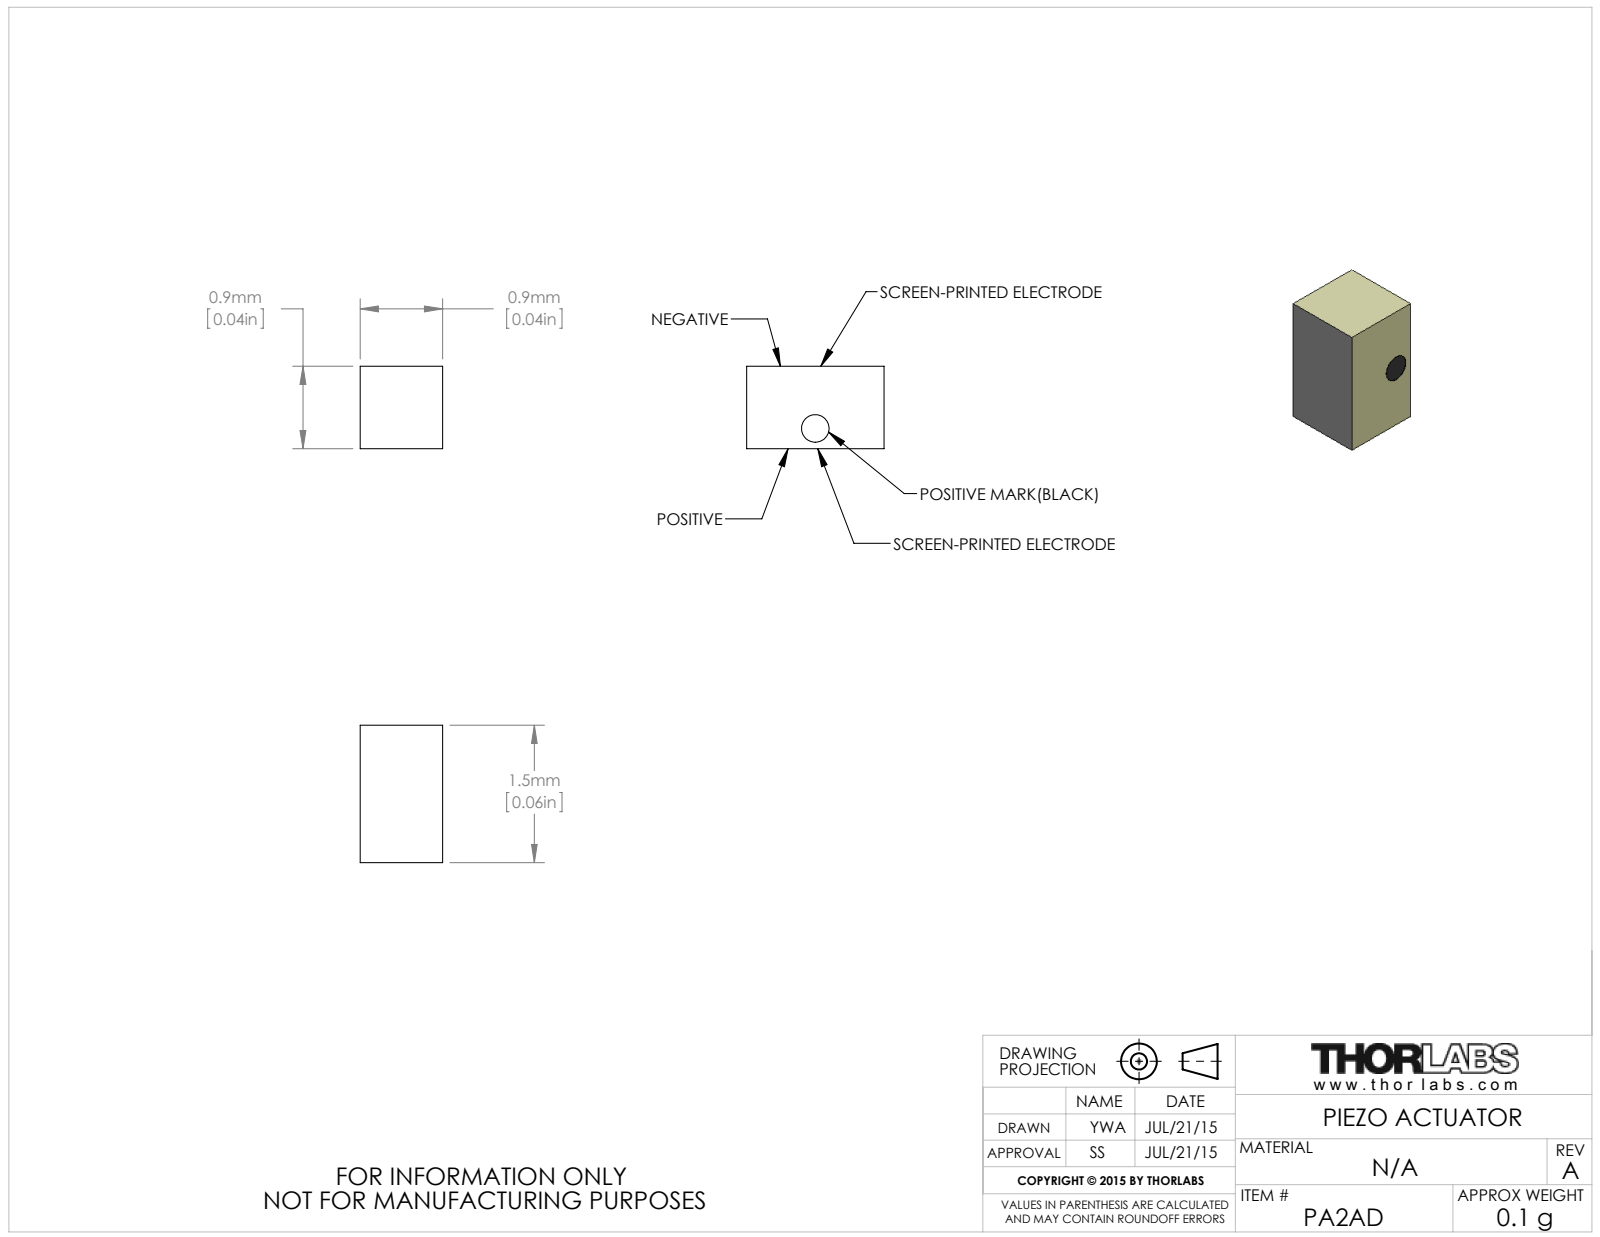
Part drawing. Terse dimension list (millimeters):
name: CTN003083
written by: SolidWorks 2014 (AUTOMOTIVE_DESIGN)
unit: mm
bodies: 1 solid, 9 faces (7 planar, 2 cylindrical, 0 other)
size: 1.5 × 0.9 × 0.9
volume: 1 mm³; area: 7 mm²
holes: 1× ⌀0.3
face distances: 0.9, 1.5, 0.89
